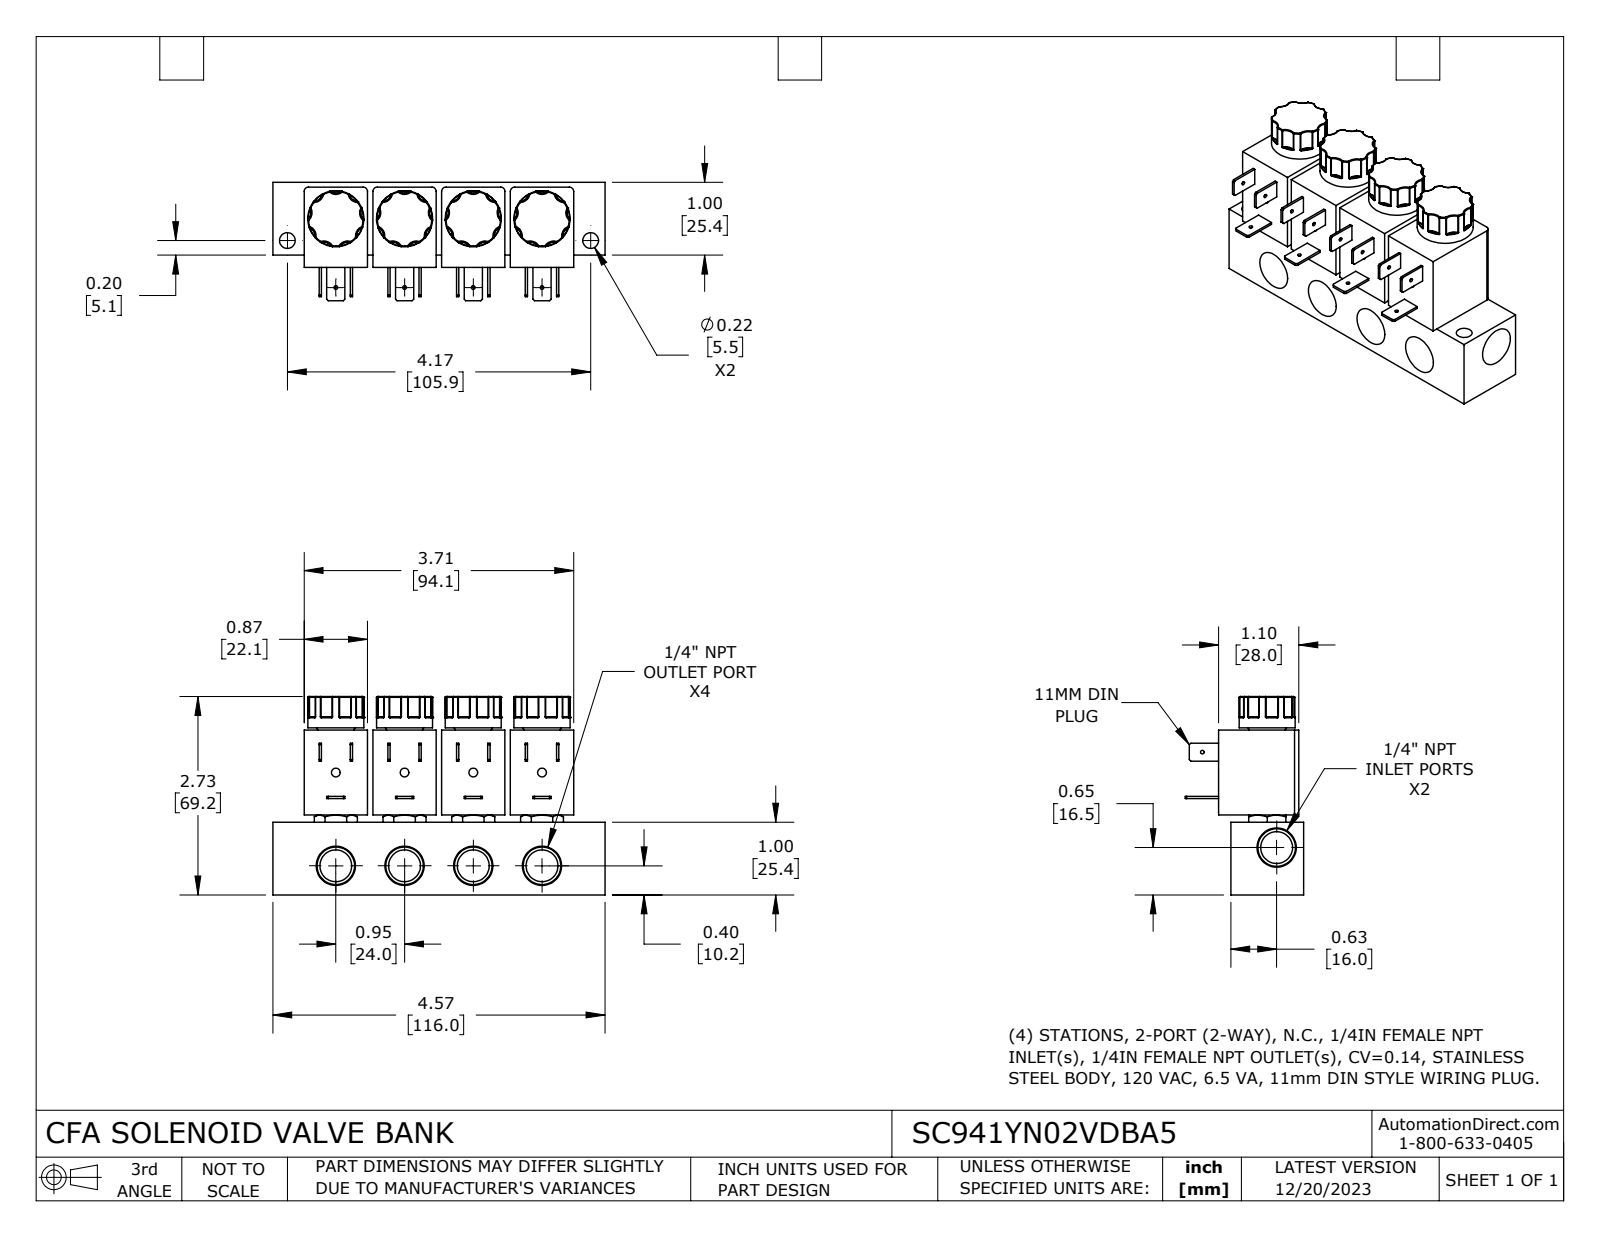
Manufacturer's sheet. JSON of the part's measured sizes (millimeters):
{"part_name": "SC941YN02VDBA5", "step_written_by": "SolidWorks 2023 (CONFIG_CONTROL_DESIGN)", "units": "millimeters", "bodies": {"solids": 1, "faces": 868, "planar": 192, "cylindrical": 184, "other": 492}, "overall_size": [116, 69.2, 41.3], "volume_mm3": 150500, "surface_area_mm2": 39390, "round_holes": [[1.3, 5], [11.1, 5], [3, 4], [5.5, 2]], "round_bosses_or_shafts": [[19.6, 4]], "partial_cylinders_radius": [[0.3, 72], [3.4, 34], [1.5, 8], [3.4, 2]], "face_to_face_distances": [25.4, 24, 29.7, 48, 46.1, 22.1, 4.3, 1.7, 23.7, 28], "hole_center_spacings": [24, 32.6, 40.5, 24, 48, 48, 72, 40.5]}
